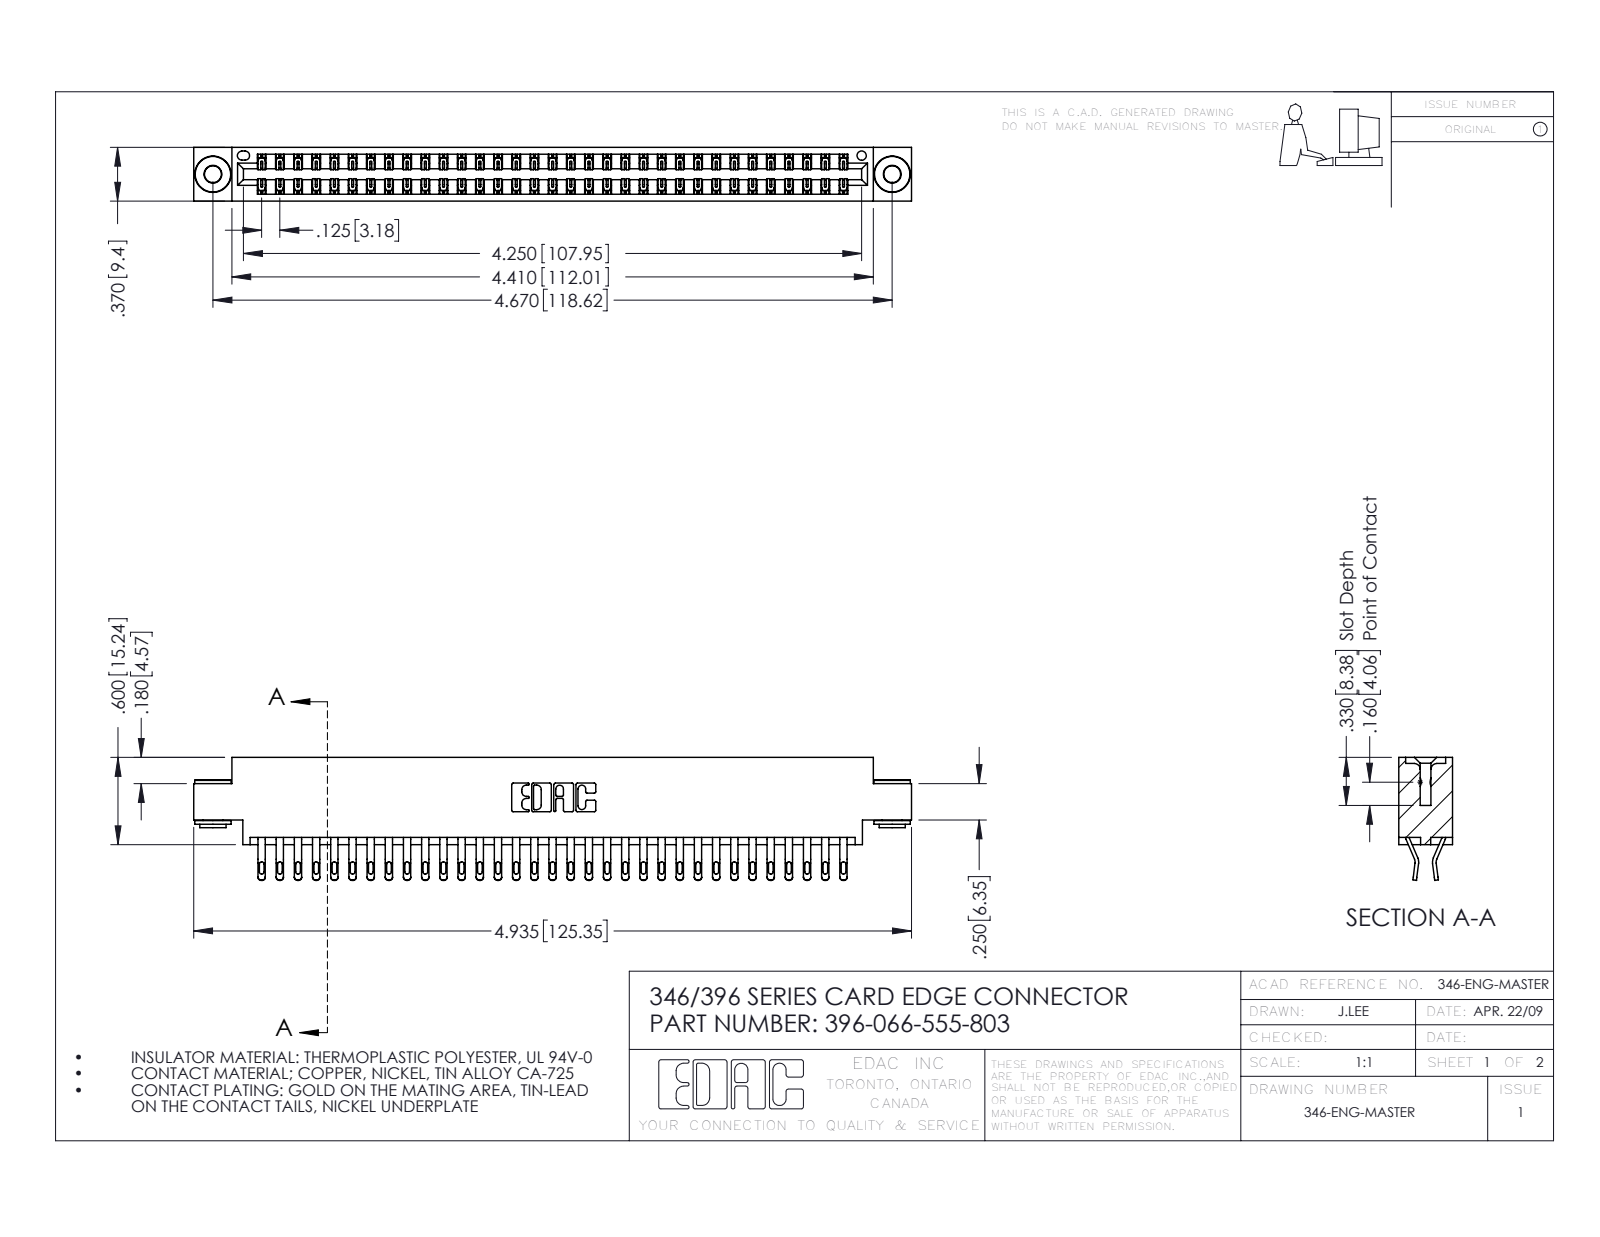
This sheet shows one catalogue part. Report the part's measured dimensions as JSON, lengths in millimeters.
{"part_name": "396-066-555-803; 345-250-002_345-250-002-102; 346 Part_0.170 Offset - 0.156 Dia-TH; 345-292-001_555 Tail", "step_written_by": "SolidWorks 2016 (CONFIG_CONTROL_DESIGN)", "units": "millimeters", "bodies": {"solids": 69, "faces": 3992, "planar": 2268, "cylindrical": 1716, "other": 8}, "overall_size": [125.3, 21.5, 9.4], "volume_mm3": 12200, "surface_area_mm2": 17720, "round_holes": [[2.9, 2], [4, 2], [1.6, 1]], "round_bosses_or_shafts": [[6.4, 2], [4.6, 2], [3.5, 2]], "partial_cylinders_radius": [[0.4, 132], [0.5, 132], [0.2, 99], [0.3, 22], [0.2, 6], [0.8, 6], [0.7, 3], [0.3, 2]], "face_to_face_distances": [1.2, 8.2, 9.4, 6.4, 0.6, 7, 1.8, 7.6, 3.8, 5.6], "hole_center_spacings": [6.2, 113.3, 118.6]}
